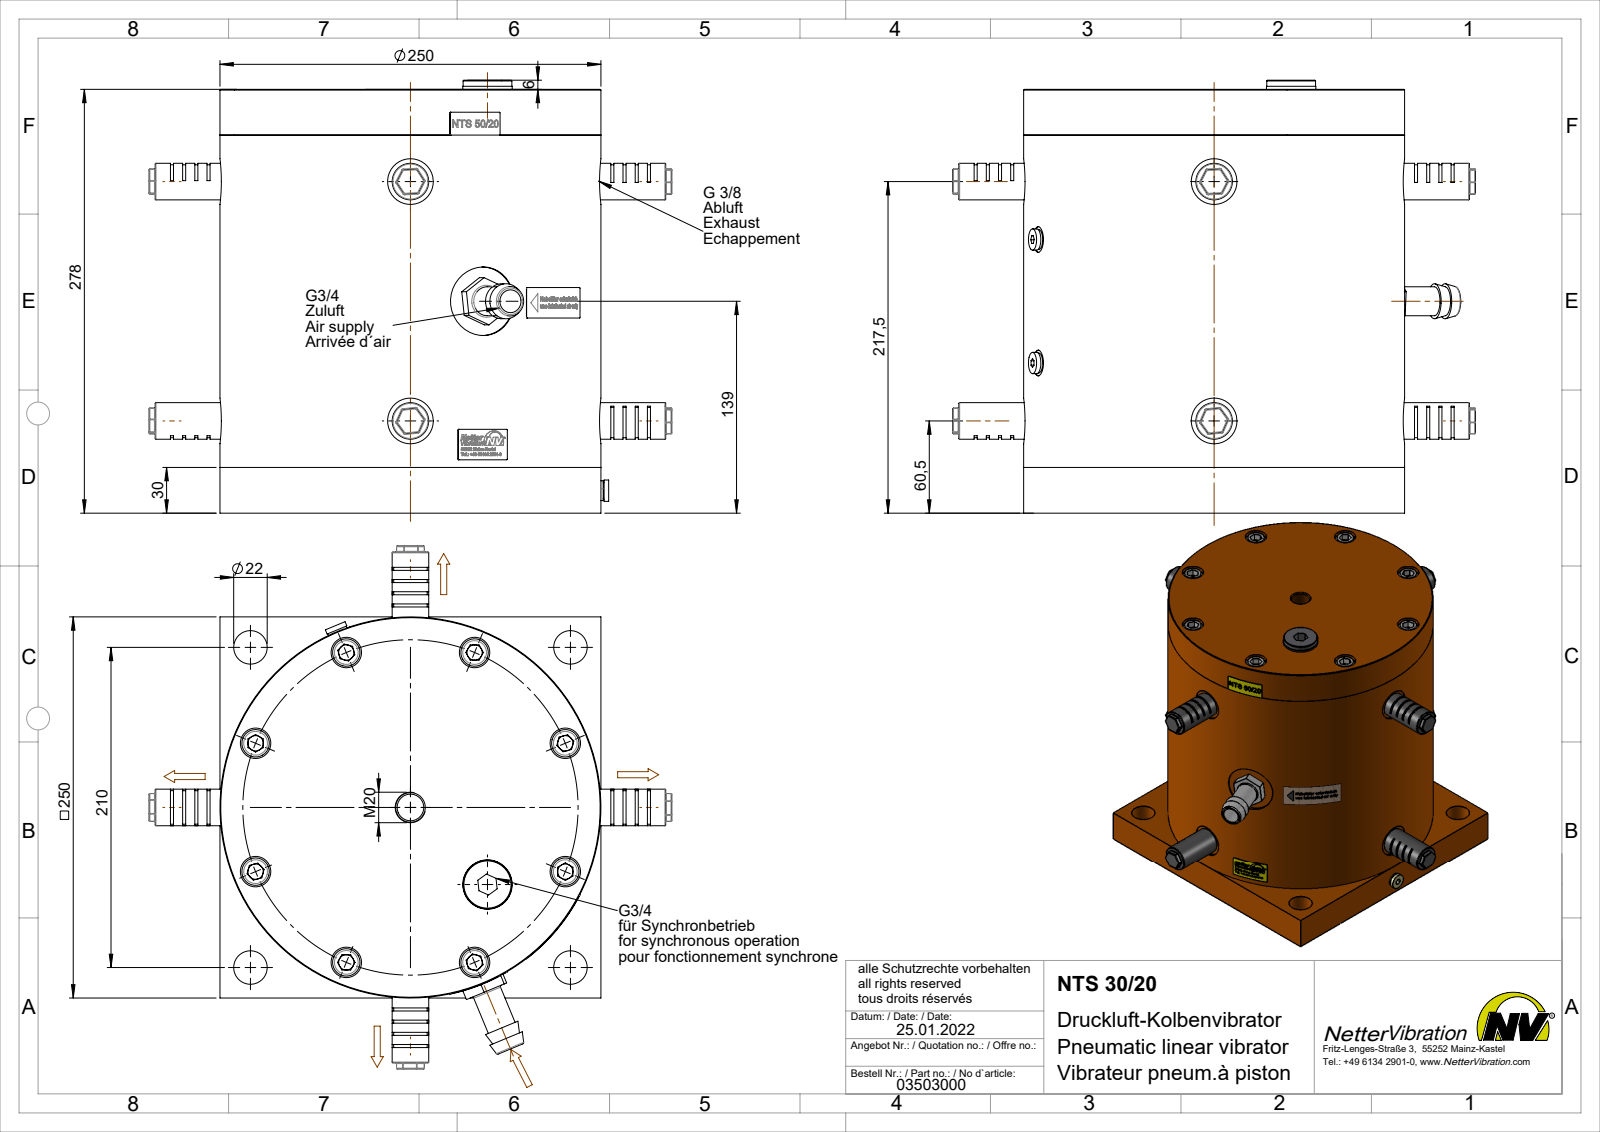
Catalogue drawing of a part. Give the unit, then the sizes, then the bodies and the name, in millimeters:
Units: millimetres
Overall size (bounding box): 343 × 343 × 284
Round holes (diameter × count): ⌀10.2 ×8, ⌀12.5 ×8, ⌀20 ×8, ⌀6 ×4, ⌀14.95 ×4, ⌀22 ×4, ⌀30 ×4, ⌀10 ×3, ⌀17 ×3, ⌀2 ×2, ⌀8.8 ×2, ⌀24.12 ×2
Round bosses / shafts (diameter × count): ⌀18 ×8, ⌀12 ×8, ⌀24 ×4, ⌀16.66 ×4, ⌀14 ×3, ⌀13 ×3, ⌀9.73 ×3, ⌀22 ×2
Partial cylindrical surfaces — rounded edges, fillets, slot ends (radius × count): R0.5 ×156, R11 ×2, R125.2 ×1
Main face-to-face distances: 218, 30, 248, 247, 29, 277, 1, 278, 250, 1.5
Hole centre spacings: 62.99, 110, 147.14, 155.57, 203.26, 215.99, 253.64, 40.5
Volume: 14 060 000 mm³ · Surface area: 712 074 mm²
Bodies: 39 solids, 1691 faces (568 planar, 709 cylindrical, 414 other)
Part name (STEP PRODUCT): NTS 30-20 Kolbenvibrator #03503000
STEP written by: SolidWorks 2015 (AUTOMOTIVE_DESIGN)
